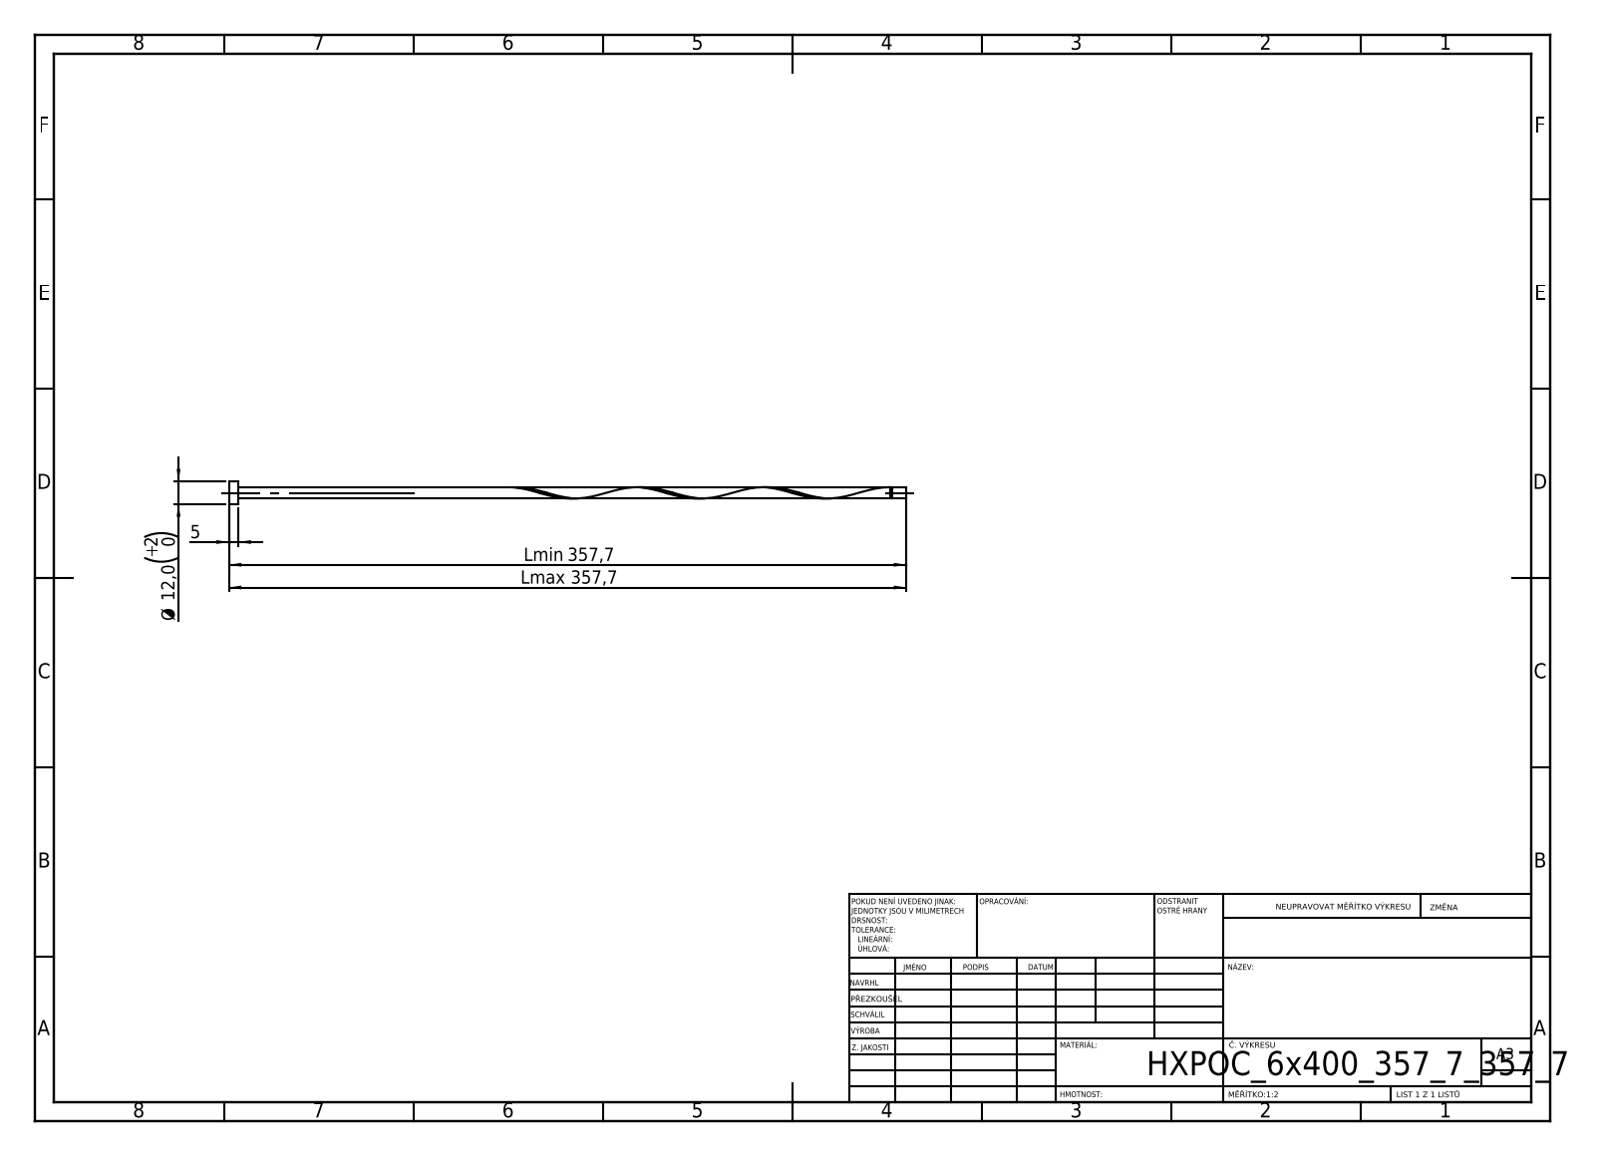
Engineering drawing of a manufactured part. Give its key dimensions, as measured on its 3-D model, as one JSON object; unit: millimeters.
{"step_written_by": "SolidWorks 2019 (CONFIG_CONTROL_DESIGN)", "units": "millimeters", "bodies": {"solids": 1, "faces": 16, "planar": 6, "cylindrical": 9, "other": 1}, "overall_size": [357.7, 12, 12], "volume_mm3": 12932, "surface_area_mm2": 9712, "round_bosses_or_shafts": [[12, 1], [6, 1], [4.8, 1]], "face_to_face_distances": [5, 357.7, 352.7, 350.44, 345.44, 7.26, 349.24, 344.24, 1.2, 8.46]}
